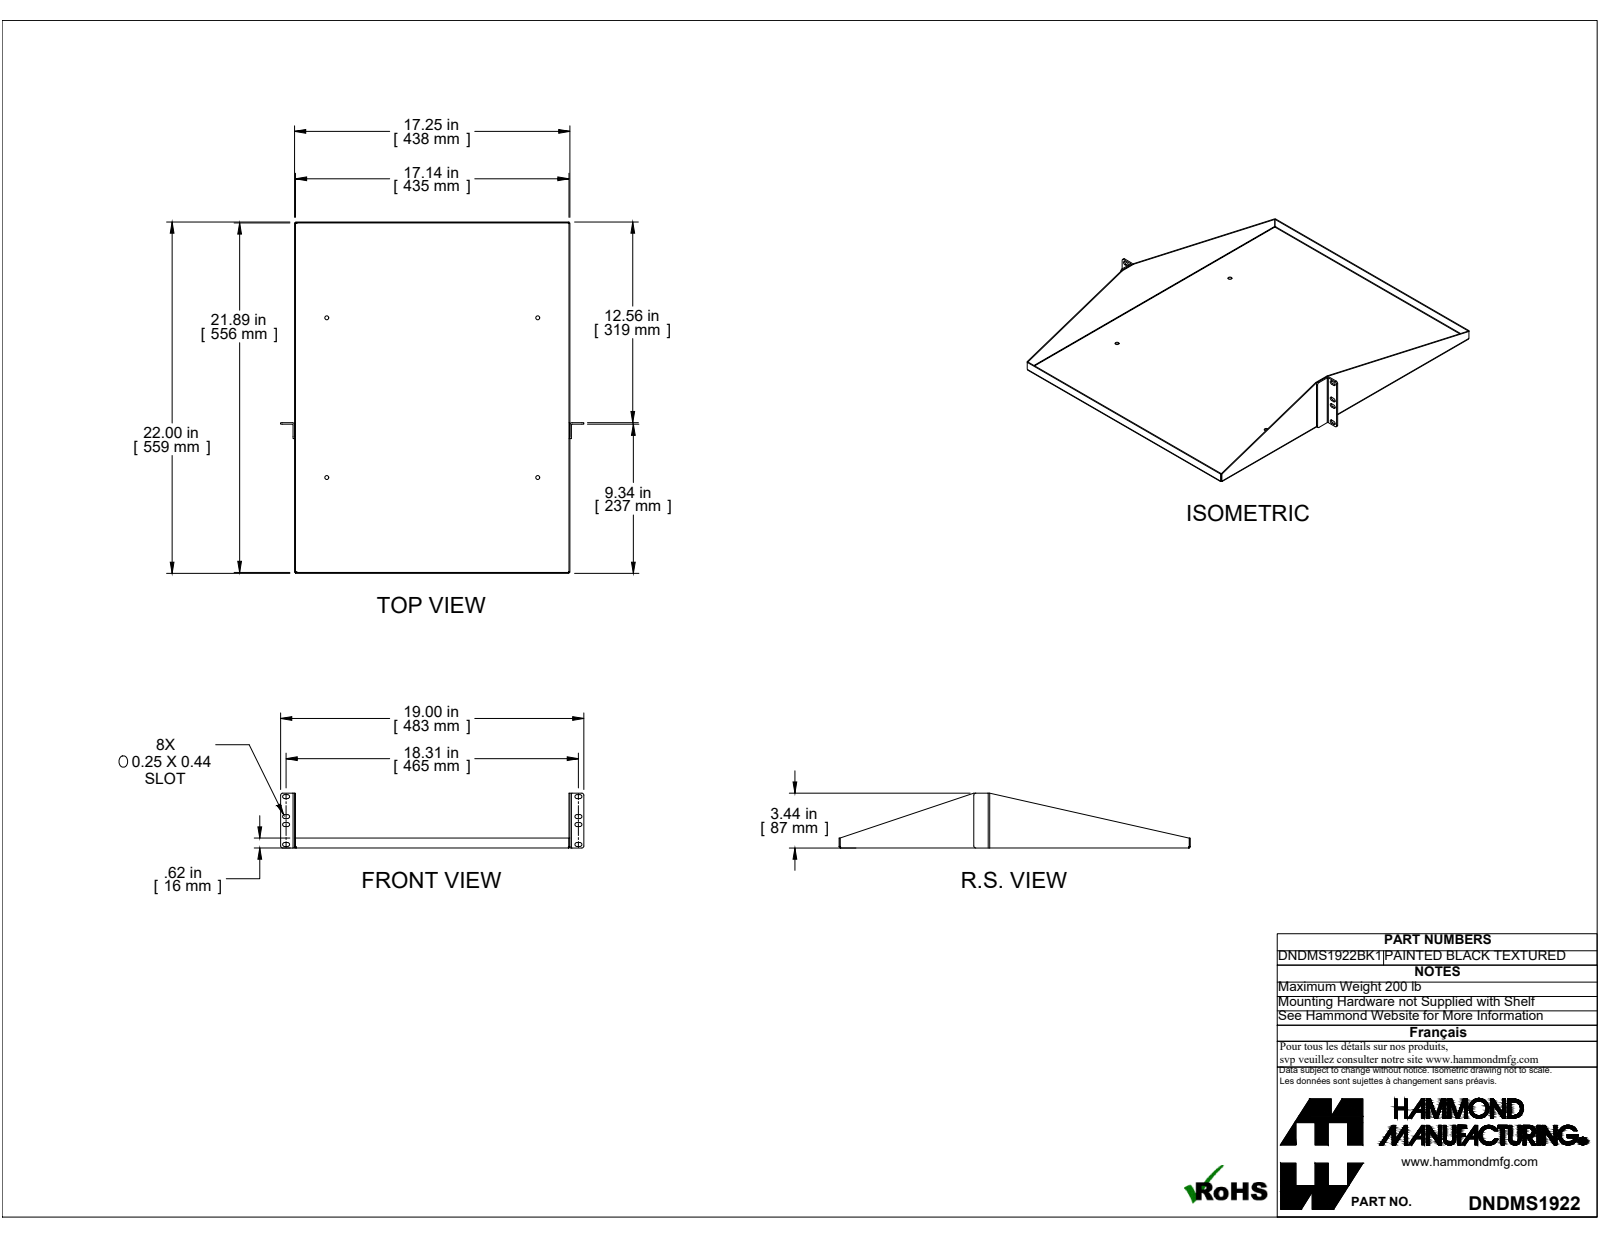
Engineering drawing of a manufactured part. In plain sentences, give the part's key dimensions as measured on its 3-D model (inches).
The part is named "DNDMS1922BK1". Its 3-D file was written by "SolidWorks 2019 (CONFIG_CONTROL_DESIGN)". It is 3 solids with 114 faces: 58 planar, 48 cylindrical and 8 other. Overall it measures 22 by 19 by 3.437 inches. Its volume is 28.76 cubic inches and its surface area 1 002 square inches. Round holes: 4 of diameter 0.25. Partial cylindrical surfaces (rounded edges, fillets, slot ends): 22 of radius 0.125, 4 of radius 0.029, 4 of radius 0.055, 4 of radius 0.086, 2 of radius 0.048, 2 of radius 0.143. The main face-to-face distances are 0.057, 0.057, 17.193, 17.25, 17.136, 21.943, 21.886, 22, 0.095, 0.152. The hole center spacings are 10, 13.218, 16.575.
